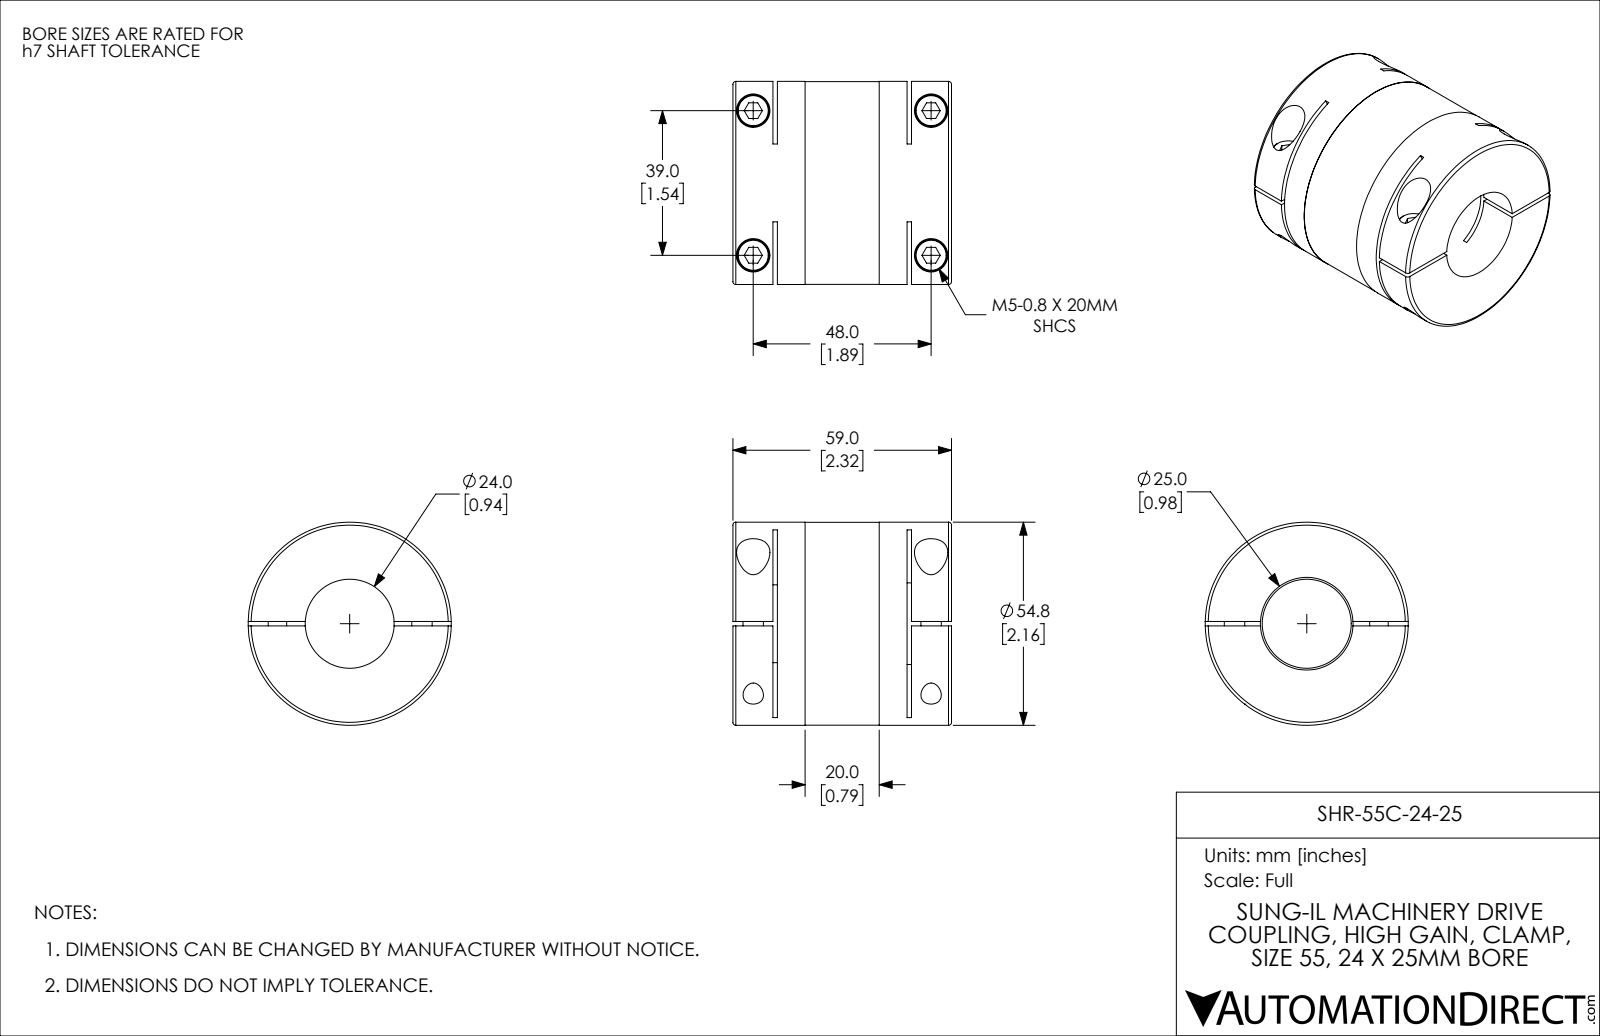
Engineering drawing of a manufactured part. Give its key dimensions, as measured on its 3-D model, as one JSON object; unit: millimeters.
{"part_name": "SHR-55C-24-25", "step_written_by": "SolidWorks 2021 (CONFIG_CONTROL_DESIGN)", "units": "millimeters", "bodies": {"solids": 1, "faces": 144, "planar": 70, "cylindrical": 58, "other": 16}, "overall_size": [59, 54.8, 54.8], "volume_mm3": 102253, "surface_area_mm2": 28451, "round_holes": [[5.5, 4], [9, 4], [24, 1], [25, 1], [27, 1]], "round_bosses_or_shafts": [[8.5, 4], [5, 2], [54.8, 1], [54.7, 1]], "partial_cylinders_radius": [[60, 2]], "face_to_face_distances": [1.2, 12, 47, 10.8, 48.2, 36.2, 59, 35, 37.4, 19.5], "hole_center_spacings": [39, 48, 61.85]}
